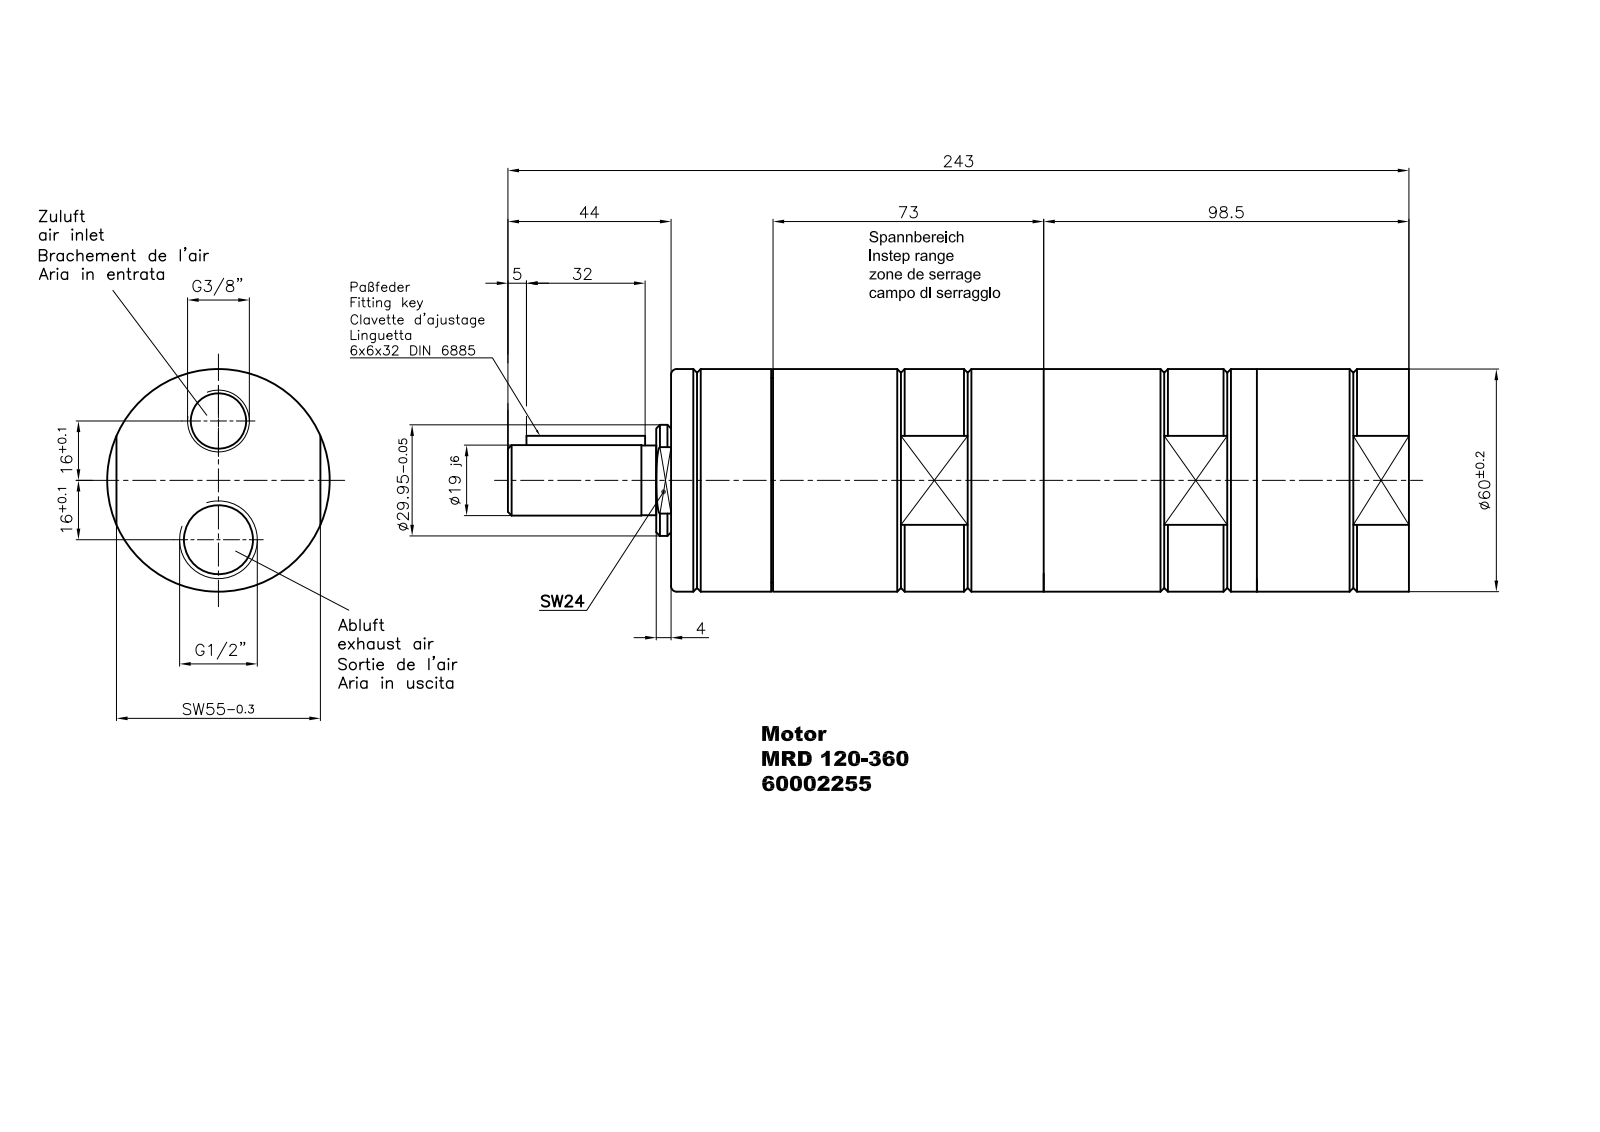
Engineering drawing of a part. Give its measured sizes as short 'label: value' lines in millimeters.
name: MRD 120-360_60002255
written by: Autodesk Inventor 2008 (CONFIG_CONTROL_DESIGN)
unit: mm
bodies: 1 solid, 120 faces (45 planar, 36 cylindrical, 39 other)
size: 243 × 60 × 60
volume: 560 019 mm³; area: 51 242 mm²
holes: 1× ⌀1.55, 1× ⌀4, 1× ⌀5.5, 1× ⌀35
bosses: 1× ⌀60, 1× ⌀58.01, 1× ⌀29.95, 1× ⌀19, 1× ⌀18.8, 1× ⌀5, 1× ⌀3.6
rounds: 2× R3, 2× R7.5, 1× R8.5, 1× R23.5, 1× R27.16
face distances: 199, 55, 181.88, 17.12, 186, 4.12, 13, 4, 185.88, 190
